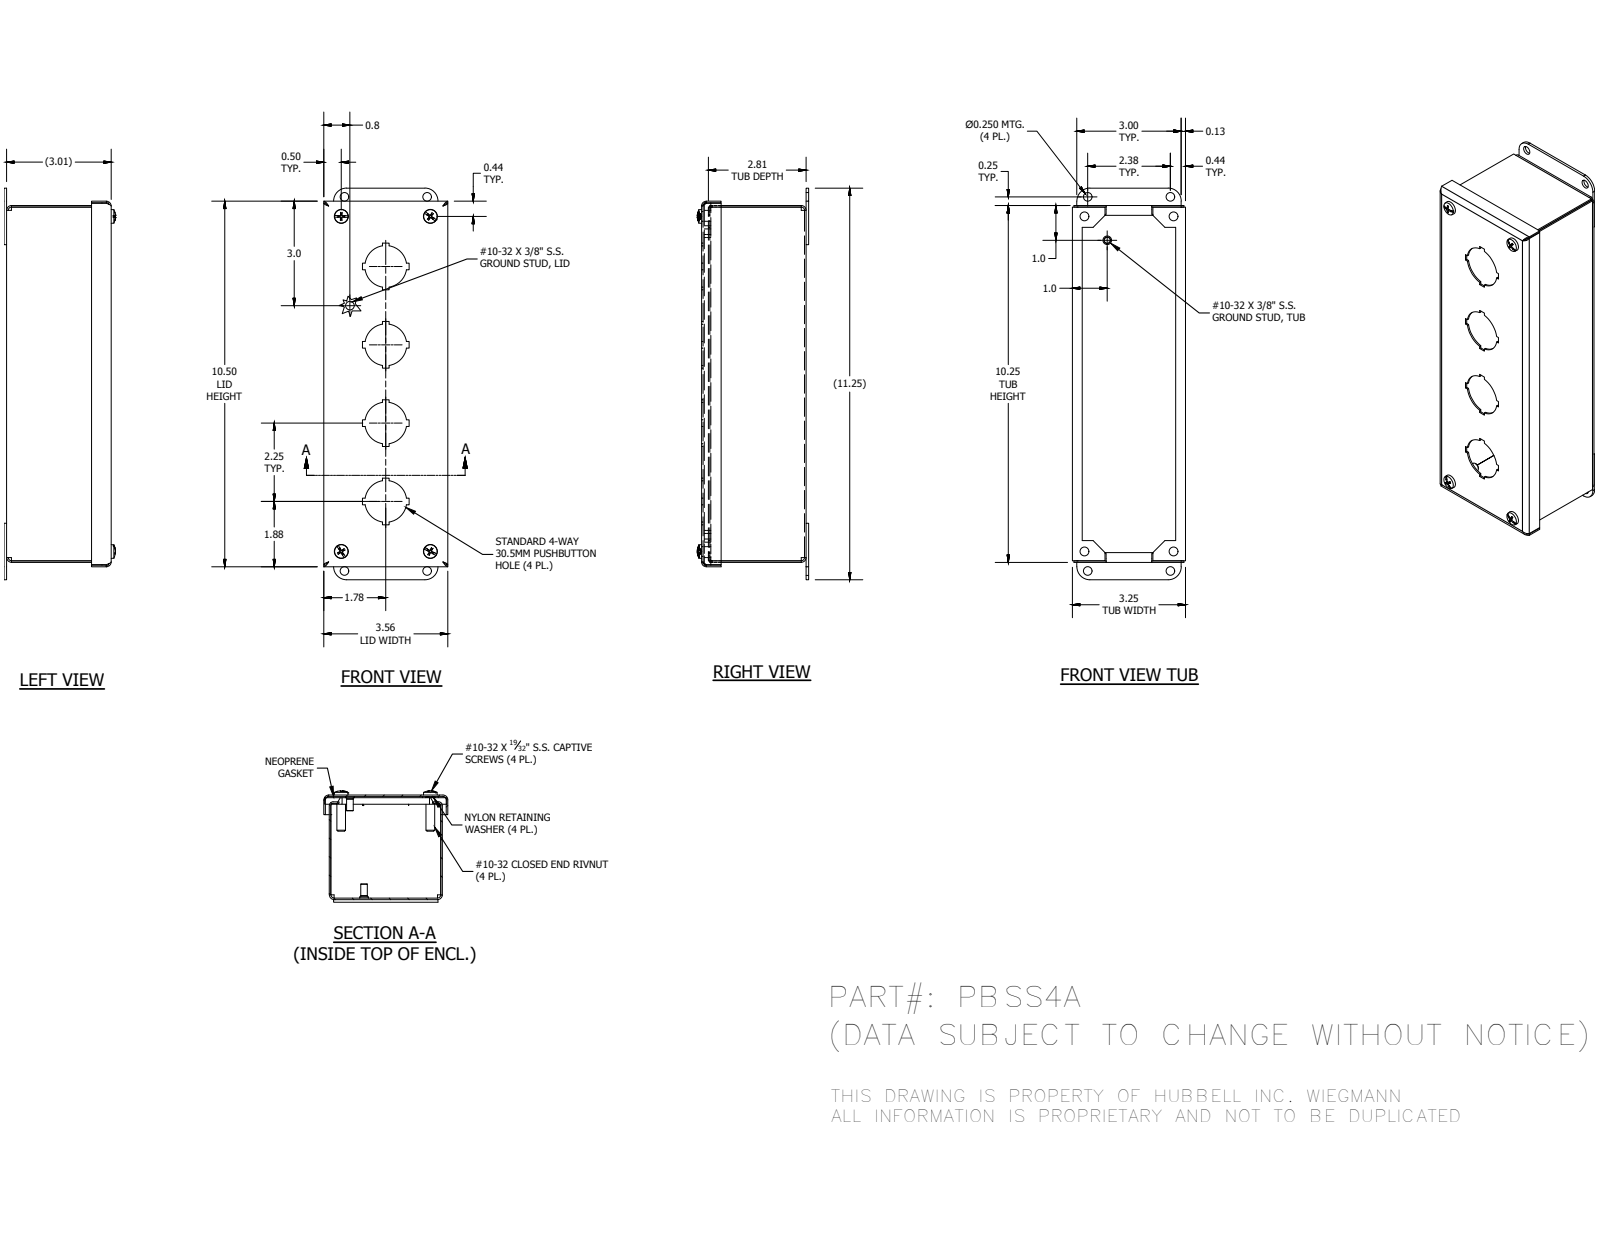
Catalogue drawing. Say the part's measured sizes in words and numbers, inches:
The part is named "PBSS4ALID; 37210; 39077; PBSS4ABKP (+5 more)". Its 3-D file was written by "Autodesk Inventor 2016 (AUTOMOTIVE_DESIGN)". It is 20 solids with 600 faces: 380 planar, 112 cylindrical and 108 other. Overall it measures 11.25 by 3.563 by 3.2 inches. Its volume is 10.62 cubic inches and its surface area 387.2 square inches. Round holes: 4 of diameter 0.156, 4 of diameter 0.196, 4 of diameter 0.25, 4 of diameter 0.257, 4 of diameter 0.278, 4 of diameter 0.281, 4 of diameter 0.313, 4 of diameter 1.2, 2 of diameter 0.133. Round bosses or shafts: 4 of diameter 0.453, 4 of diameter 0.406, 4 of diameter 0.248, 4 of diameter 0.167, 2 of diameter 0.25, 2 of diameter 0.19. Partial cylindrical surfaces (rounded edges, fillets, slot ends): 8 of radius 0.094, 8 of radius 0.139, 4 of radius 0.089, 4 of radius 0.375, 3 of radius 0.063, 3 of radius 0.107, 1 of radius 0.063, 1 of radius 0.107. The main face-to-face distances are 0.045, 0.045, 2.915, 2.96, 2.96, 3.005, 3.205, 3.16, 3.205, 3.25. The hole center spacings are 0.019, 1.926, 3.904, 6.074, 8.287, 8.83, 9.643, 10.188.
